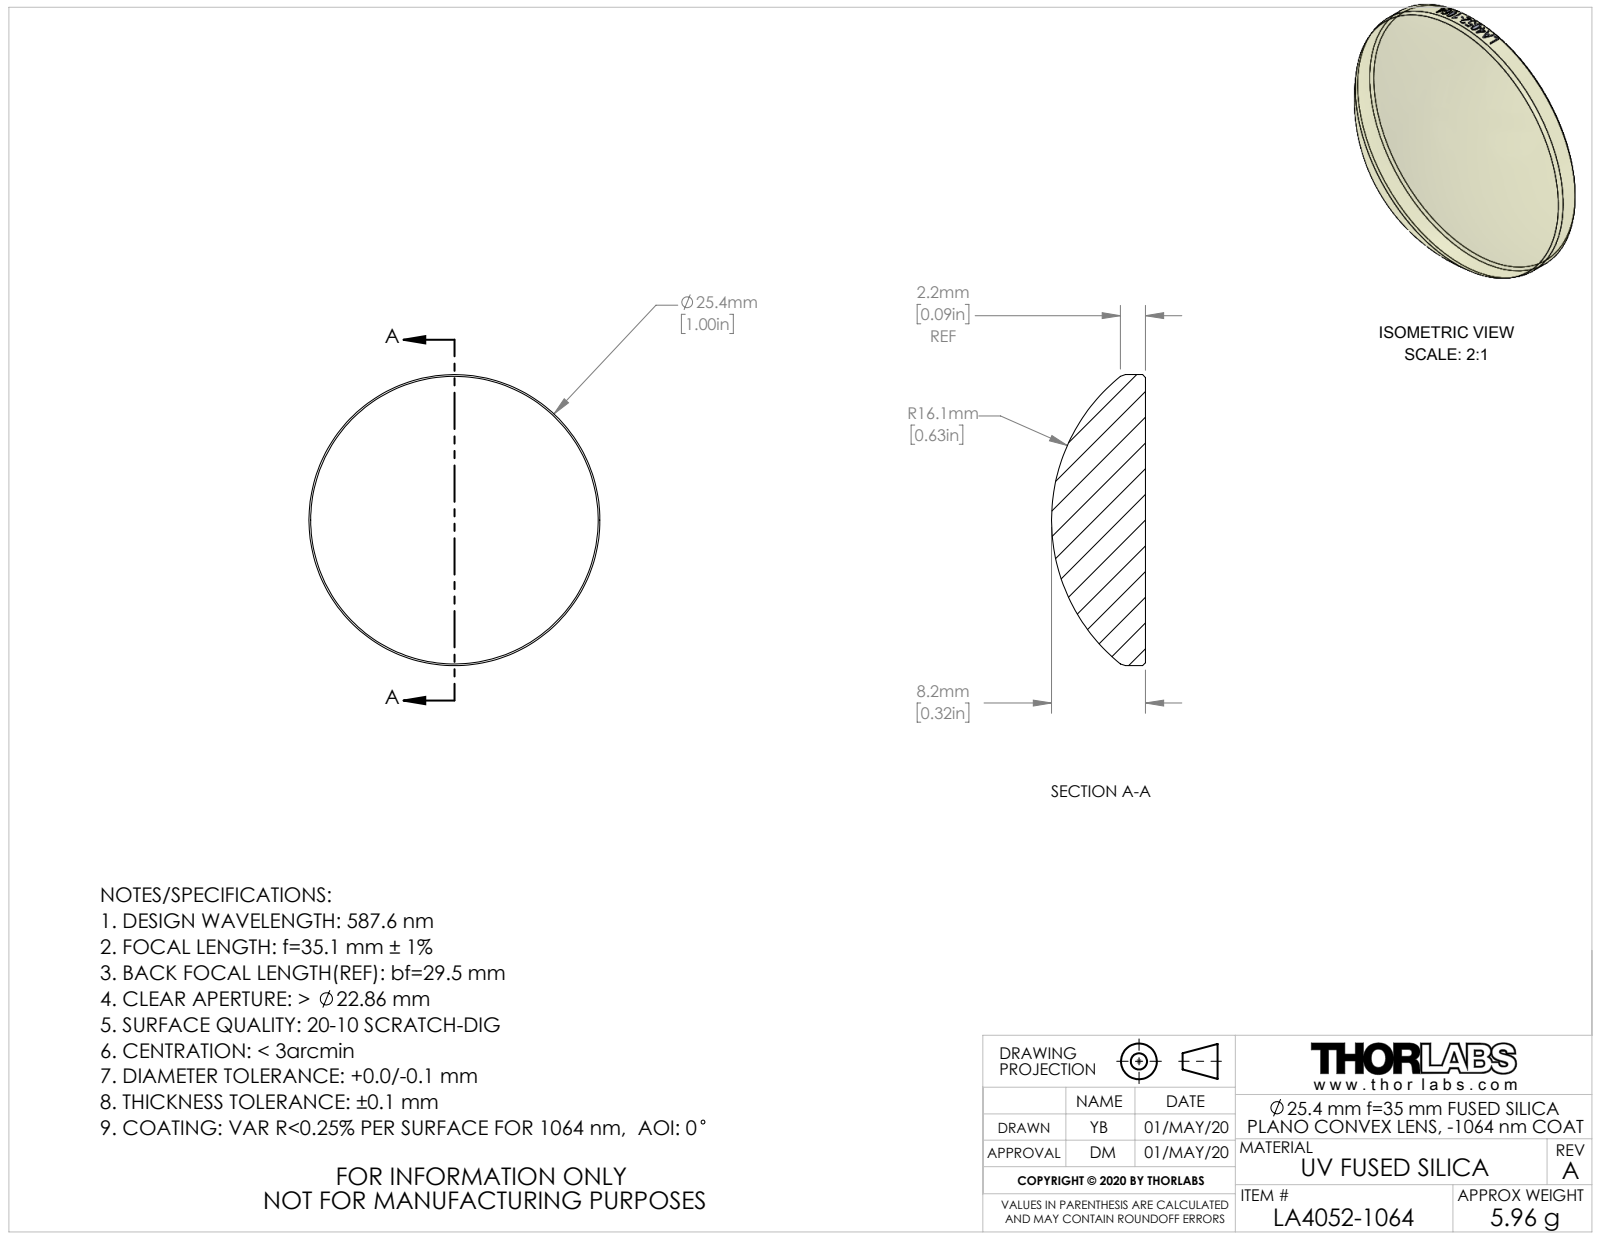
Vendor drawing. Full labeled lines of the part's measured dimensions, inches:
Part name (STEP PRODUCT): CTN015553-E0W
STEP written by: SolidWorks 2018 (AUTOMOTIVE_DESIGN)
Units: inches
Bodies: 1 solid, 26 faces (1 planar, 19 cylindrical, 6 other)
Overall size (bounding box): 1 × 1 × 0.323
Volume: 0.165 in³ · Surface area: 1.984 in²
Round bosses / shafts (diameter × count): ⌀1 ×1
